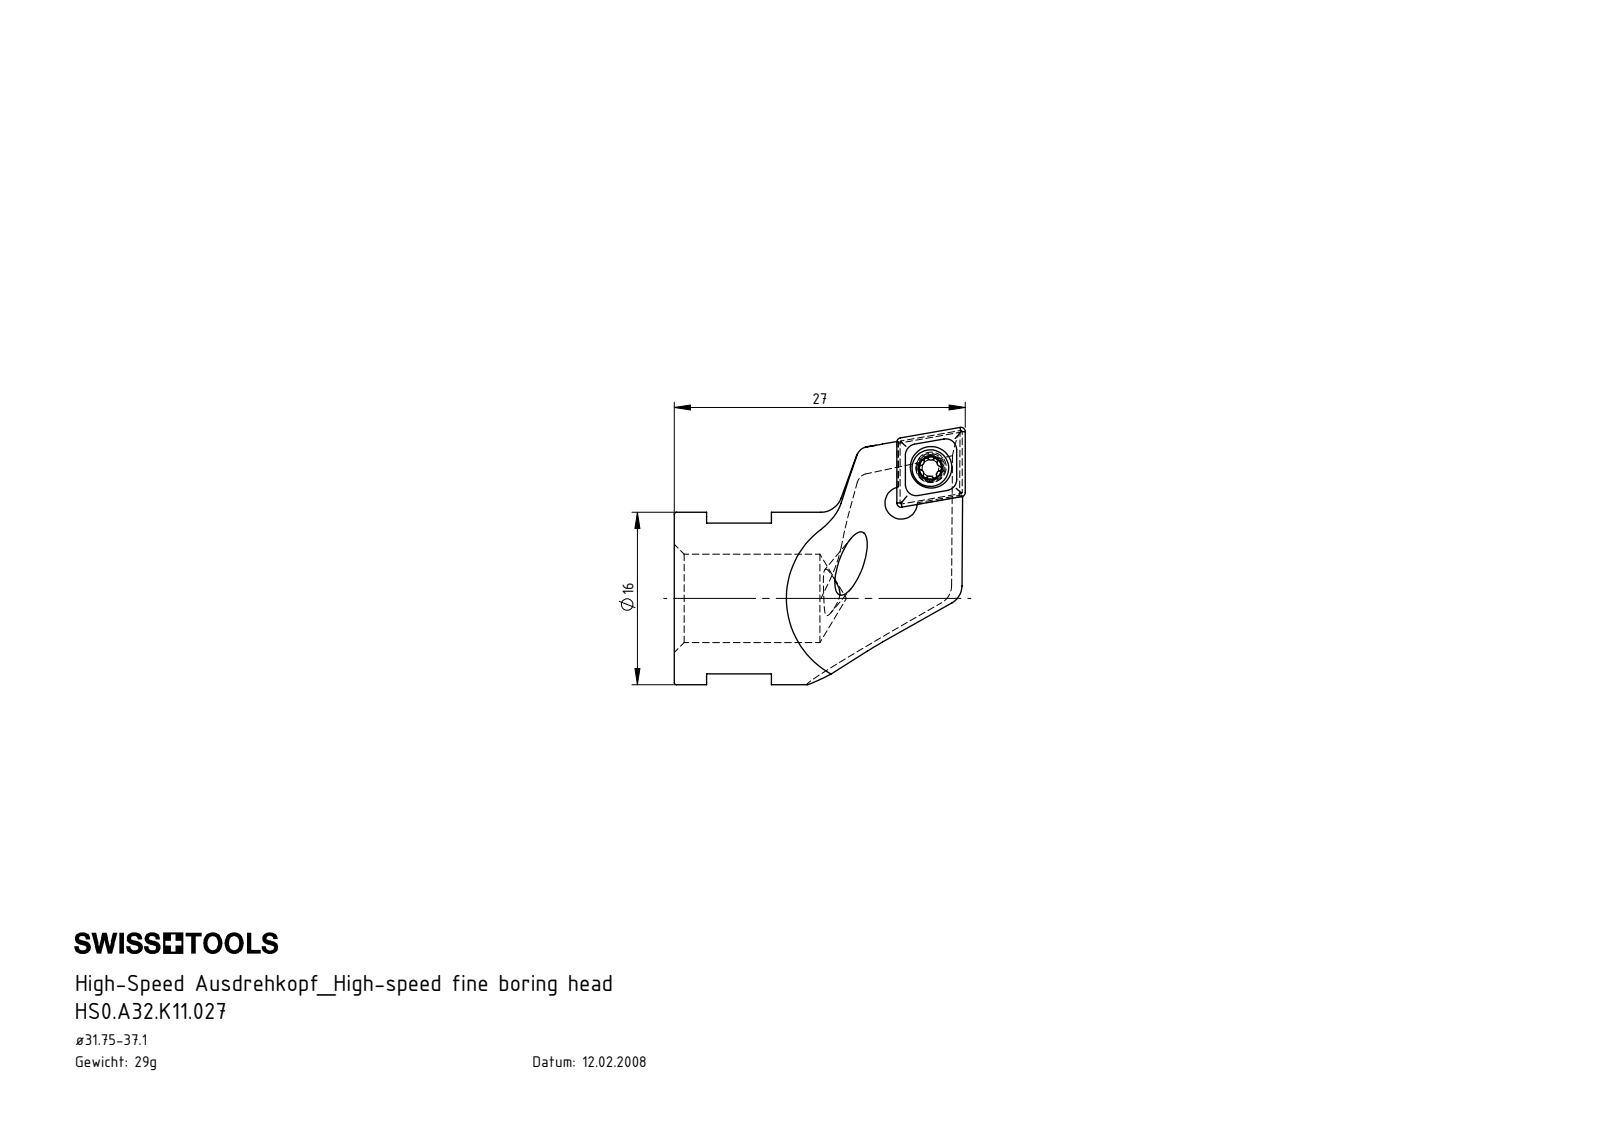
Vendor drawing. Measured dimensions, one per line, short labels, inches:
name: WCA-ER2.001.006_A; CCMT060204; HS0.A32.K11.027; HS0-A32.K11.027_B
written by: SolidWorks 2017 (AUTOMOTIVE_DESIGN)
unit: in
bodies: 3 solids, 123 faces (34 planar, 35 cylindrical, 54 other)
size: 1.063 × 0.94 × 0.63
volume: 0.219 in³; area: 3.585 in²
holes: 1× ⌀0.081, 1× ⌀0.11, 1× ⌀0.118, 1× ⌀0.152, 1× ⌀0.323
bosses: 1× ⌀0.63, 1× ⌀0.134, 1× ⌀0.098
rounds: 6× R0.008, 4× R0.014, 2× R0.014, 1× R0.059, 1× R0.071, 1× R0.079
face distances: 0.311, 0.221, 0.09, 0.551, 0.236, 0.315, 0.094, 0.354, 0.118, 0.819
